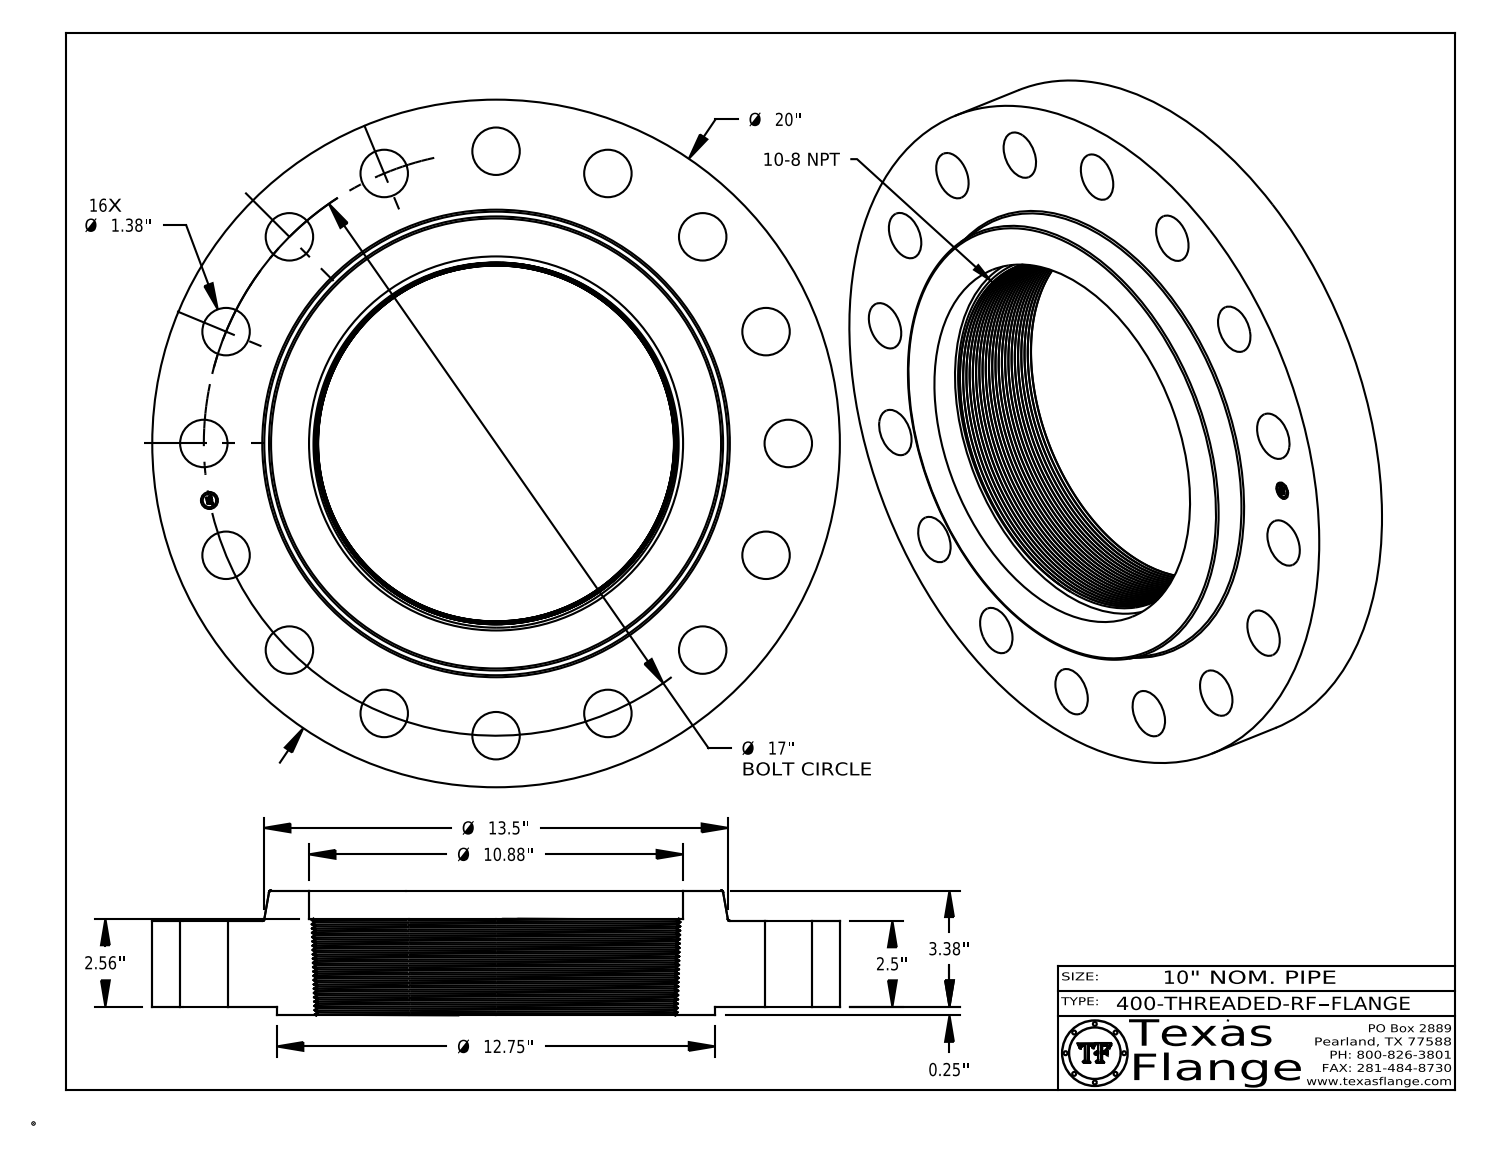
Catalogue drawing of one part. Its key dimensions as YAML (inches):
part_name: "400-THREADED-RF"
step_written_by: "CATIA V5 STEP AP214 (AUTOMOTIVE_DESIGN)"
units: inches
bodies: {solids: 1, faces: 665, planar: 370, cylindrical: 58, other: 237}
overall_size: [20, 20, 3.63]
volume: 559.5
surface_area: 978.8
round_holes:
  - {diameter: 1.38, count: 16}
  - {diameter: 0.495, count: 1}
  - {diameter: 10.88, count: 1}
round_bosses_or_shafts:
  - {diameter: 0.03, count: 8}
  - {diameter: 20, count: 1}
  - {diameter: 12.75, count: 1}
  - {diameter: 0.39, count: 1}
face_to_face_distances: [2.5, 0.25, 2.75, 3.63, 3.38, 0.88, 2.81, 2.56, 0.06, 0.82]
hole_center_spacings: [3.317, 14.135, 8.5, 6.506, 12.021, 9.444, 9.445, 15.706]
